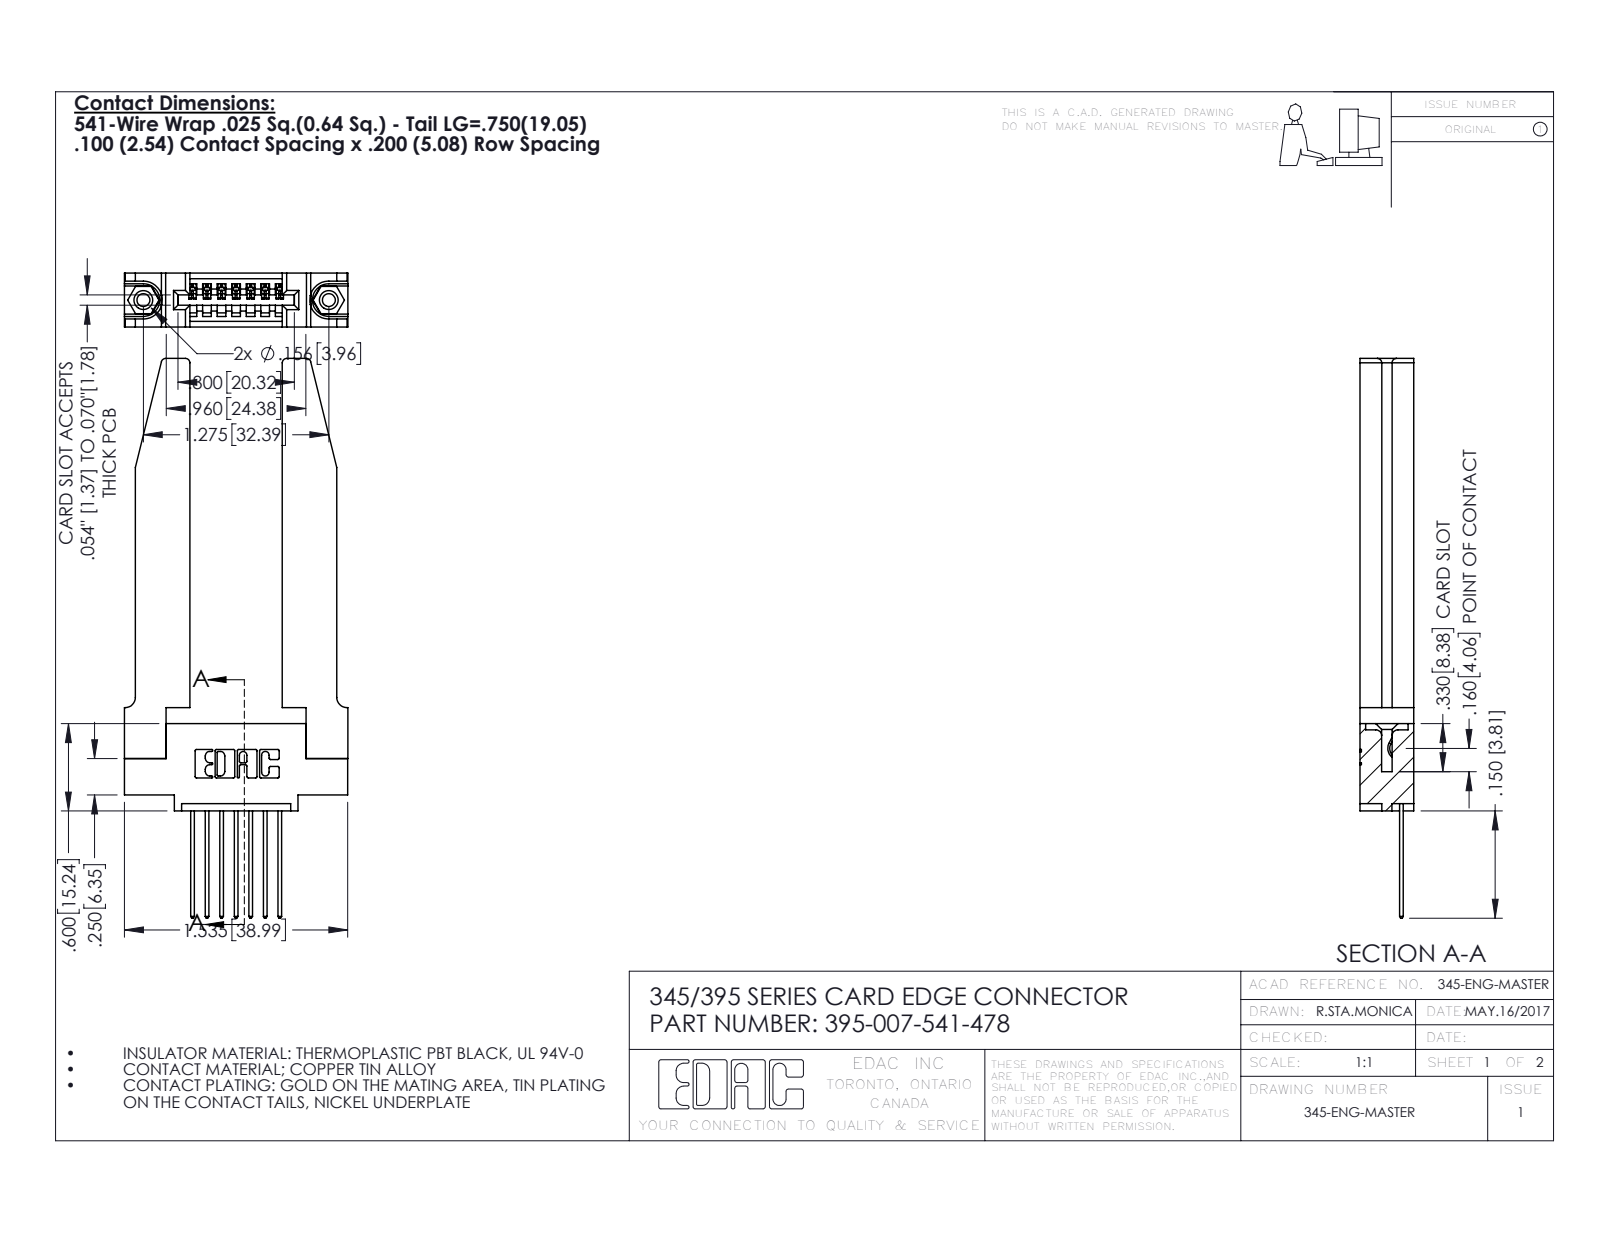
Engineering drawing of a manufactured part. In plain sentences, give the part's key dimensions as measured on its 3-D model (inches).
The part is named "345 Part_0.110 Offset - 0.156 Dia-TH; 345-250-001_345-250-001-102; 345-220-078_345-220-078; 345-292-001_345-293-141 (+1 more)". Its 3-D file was written by "SolidWorks 2016 (CONFIG_CONTROL_DESIGN)". It is 12 solids with 770 faces: 506 planar, 212 cylindrical and 52 other. Overall it measures 3.847 by 1.536 by 0.37 inches. Its volume is 0.68 cubic inches and its surface area 17.15 square inches. Round holes: 2 of diameter 0.089, 2 of diameter 0.125, 2 of diameter 0.156, 1 of diameter 0.064. Round bosses or shafts: 2 of diameter 0.155. Partial cylindrical surfaces (rounded edges, fillets, slot ends): 22 of radius 0.01, 14 of radius 0.006, 14 of radius 0.01, 8 of radius 0.03, 6 of radius 0.007, 6 of radius 0.031, 3 of radius 0.026, 2 of radius 0.031. The main face-to-face distances are 0.37, 0.15, 0.072, 0.22, 0.298, 0.148, 0.635, 0.077, 0.2, 0.098. The hole center spacings are 0.27, 1.045, 1.275.
